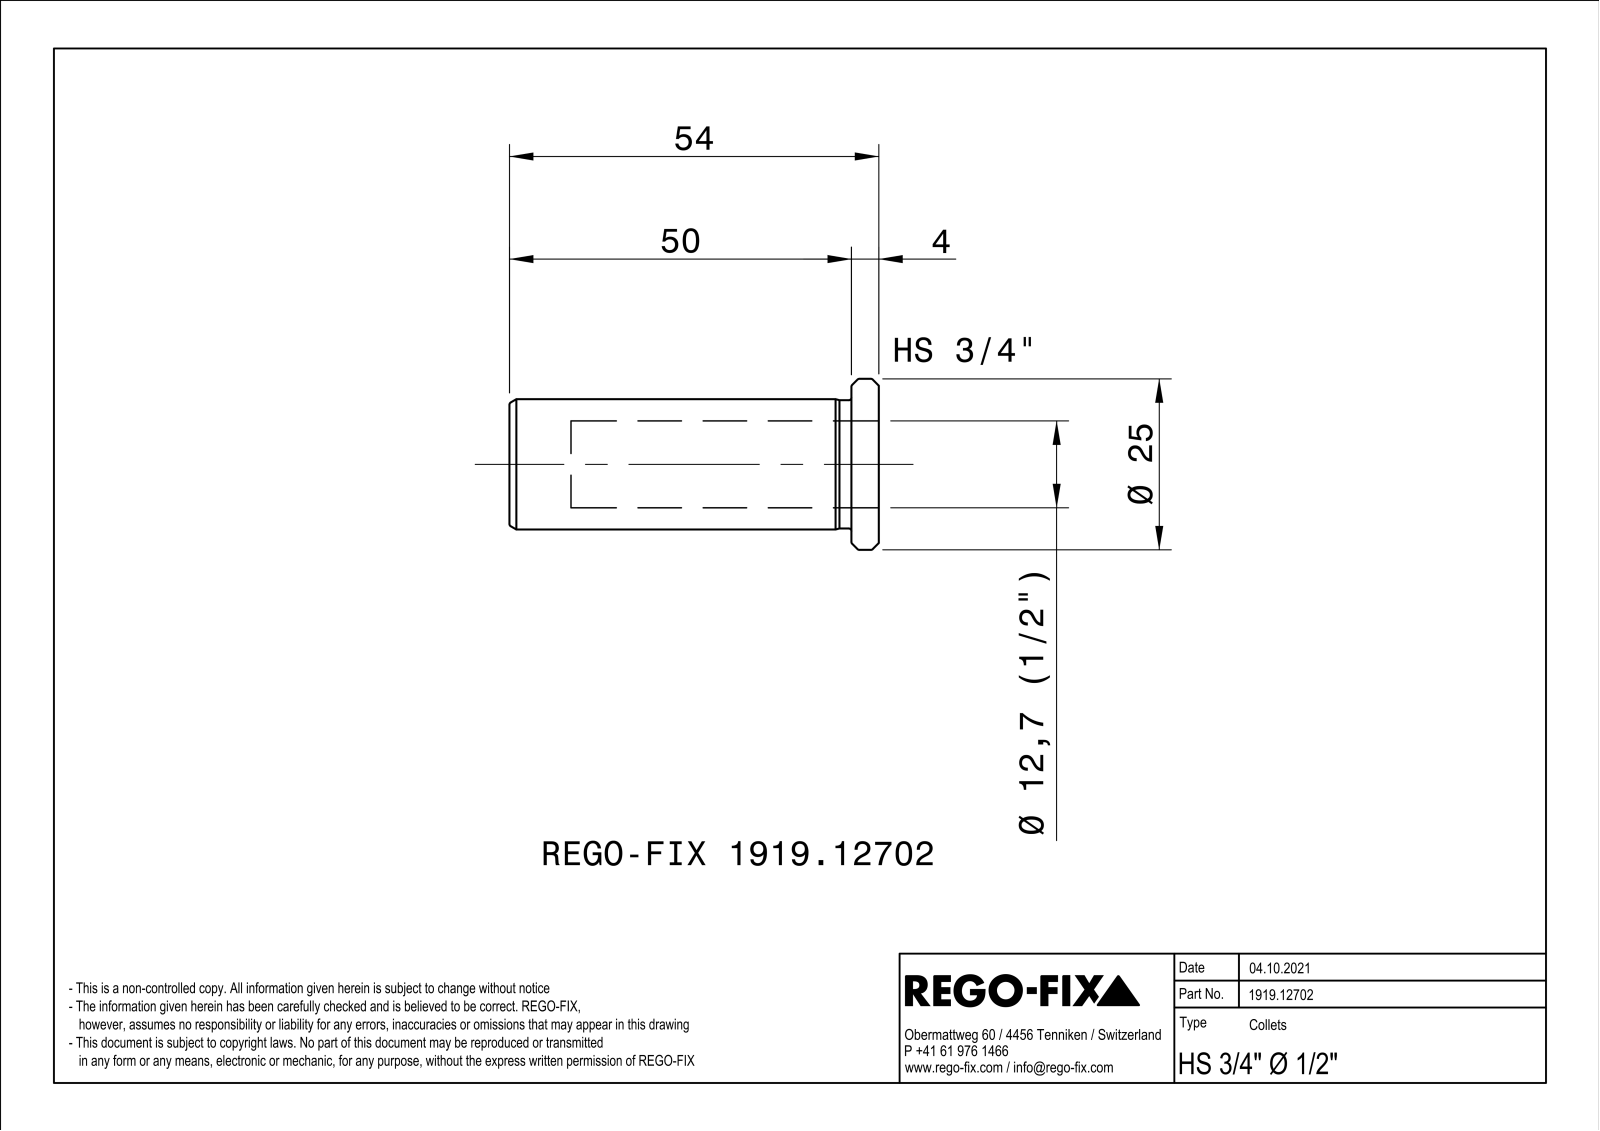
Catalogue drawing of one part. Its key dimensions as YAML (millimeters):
part_name: "NOCUT"
step_written_by: "SIEMENS PLM Software Solid Edge ST10 (AUTOMOTIVE_DESIGN)"
units: millimeters
bodies: {solids: 1, faces: 233, planar: 150, cylindrical: 12, other: 71}
overall_size: [54, 24.98, 24.98]
volume: 6865
surface_area: 6836
round_holes:
  - {diameter: 14, count: 1}
  - {diameter: 16.5, count: 1}
round_bosses_or_shafts:
  - {diameter: 25, count: 1}
  - {diameter: 19.05, count: 1}
  - {diameter: 18.75, count: 1}
partial_cylinders:
  - {radius: 378.53, count: 1}
face_to_face_distances: [1, 4, 3.99, 54, 53.99, 50, 1.26, 1.52, 1.86, 0.44]
